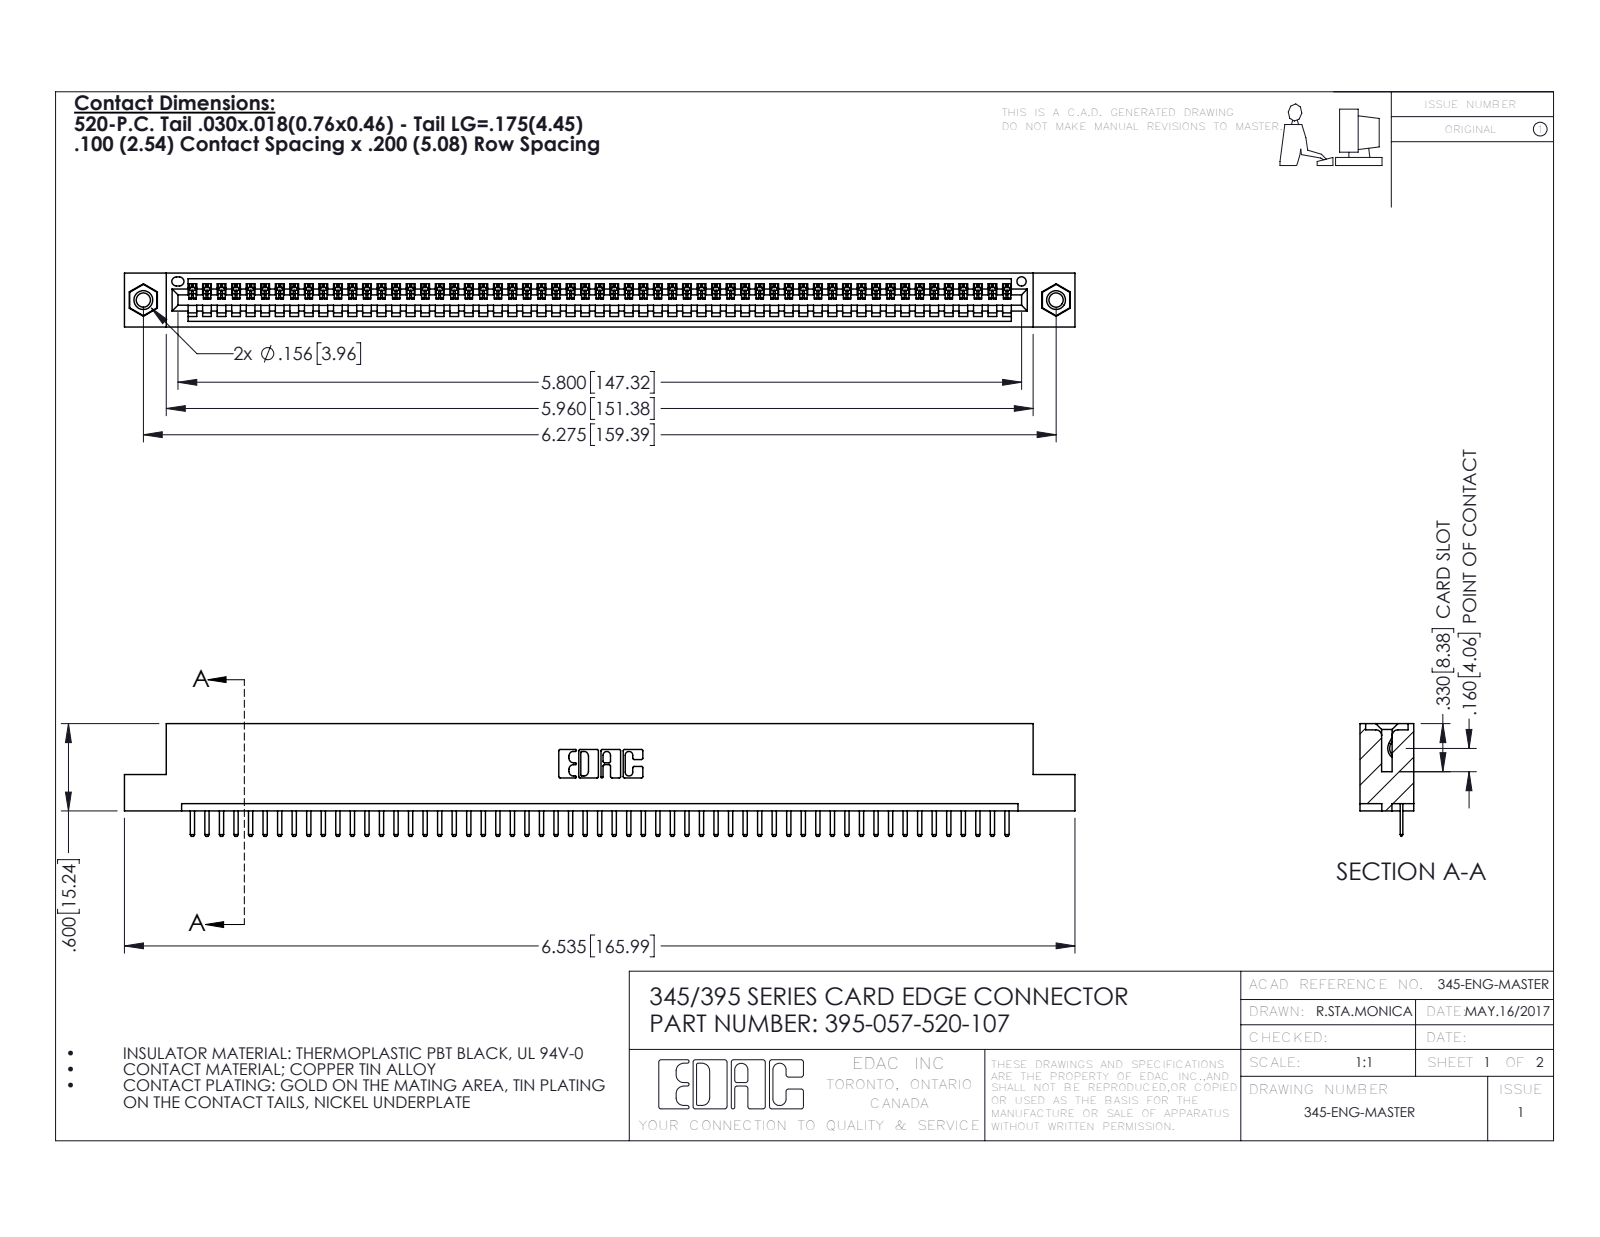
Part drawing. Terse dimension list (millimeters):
name: 345 Part_Flush Mounting Lugs - 0.156 Dia-TI; 395-057-520-107; 345-292-001_345-293-120; 345-250-001_345-250-005-103
written by: SolidWorks 2016 (CONFIG_CONTROL_DESIGN)
unit: mm
bodies: 60 solids, 3720 faces (2506 planar, 1198 cylindrical, 16 other)
size: 166 × 19.7 × 9.4
volume: 15 700 mm³; area: 20 580 mm²
holes: 2× ⌀2.5, 2× ⌀3.2, 2× ⌀4, 1× ⌀1.6
bosses: 2× ⌀3.9
rounds: 116× R0.3, 114× R0.2, 22× R0.3, 6× R0.2, 6× R0.8, 3× R0.7, 2× R0.8, 2× R1
face distances: 1.8, 7.6, 9.4, 5.1, 2.5, 6.9, 0.6, 5.7, 1.8, 3.8
hole spacings: 6.9, 153.4, 159.4
